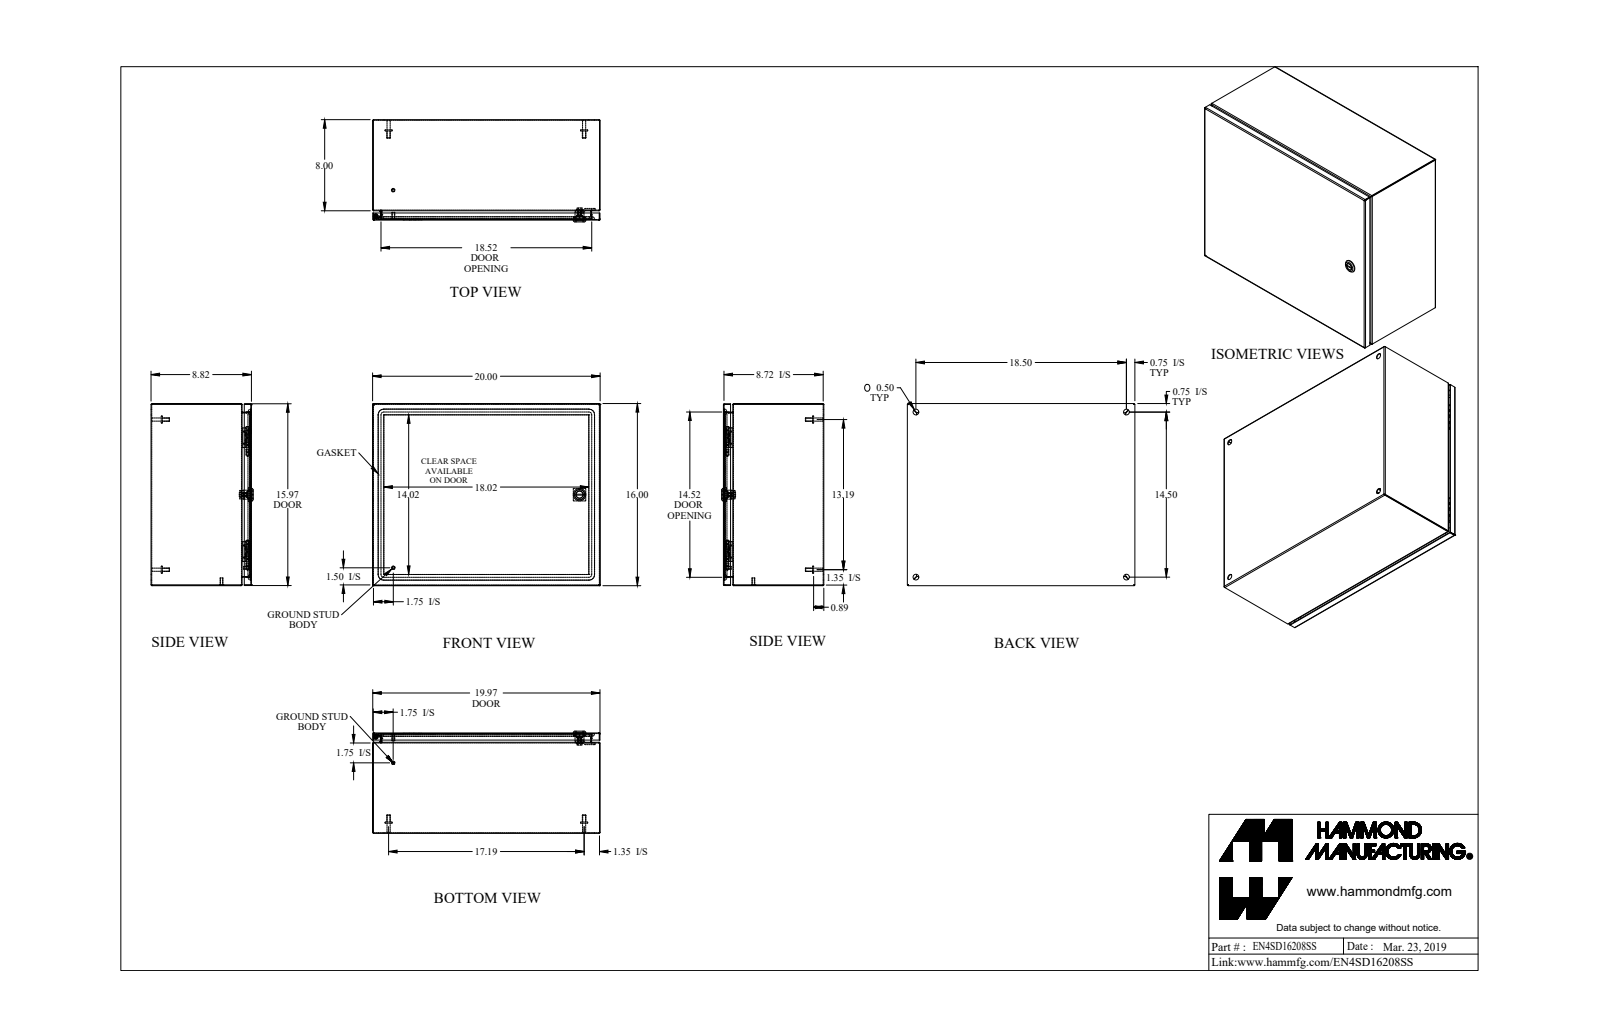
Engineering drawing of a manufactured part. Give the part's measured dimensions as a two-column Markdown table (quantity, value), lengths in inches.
| quantity | value |
| --- | --- |
| part name | EN4SD16208SS_Default |
| STEP written by | SolidWorks 2019 (CONFIG_CONTROL_DESIGN) |
| units | inches |
| bodies | 22 solids, 657 faces (303 planar, 212 cylindrical, 142 other) |
| overall size | 20 × 16 × 8.982 |
| volume | 84.46 in³ |
| surface area | 2 875 in² |
| round holes (diameter × count) | 0.5 × 5, 0.172 × 1, 0.197 × 1, 0.24 × 1, 0.242 × 1, 0.387 × 1, 0.63 × 1, 0.768 × 1 |
| round bosses / shafts (diameter × count) | 0.313 × 6, 0.625 × 5, 0.275 × 4, 0.25 × 2, 1.1 × 1, 0.785 × 1, 0.525 × 1, 0.455 × 1 |
| partial cylindrical surfaces (radius × count) | 0.029 × 21, 0.086 × 21, 0.188 × 12, 0.006 × 4, 0.062 × 4, 0.25 × 4, 0.499 × 4, 0.125 × 2 |
| main face-to-face distances | 0.057, 8.765, 8.708, 8.822, 15.943, 19.943, 15.886, 16, 19.886, 20 |
| hole center spacings | 7.327, 14.5, 18.5, 18.888, 23.506 |
